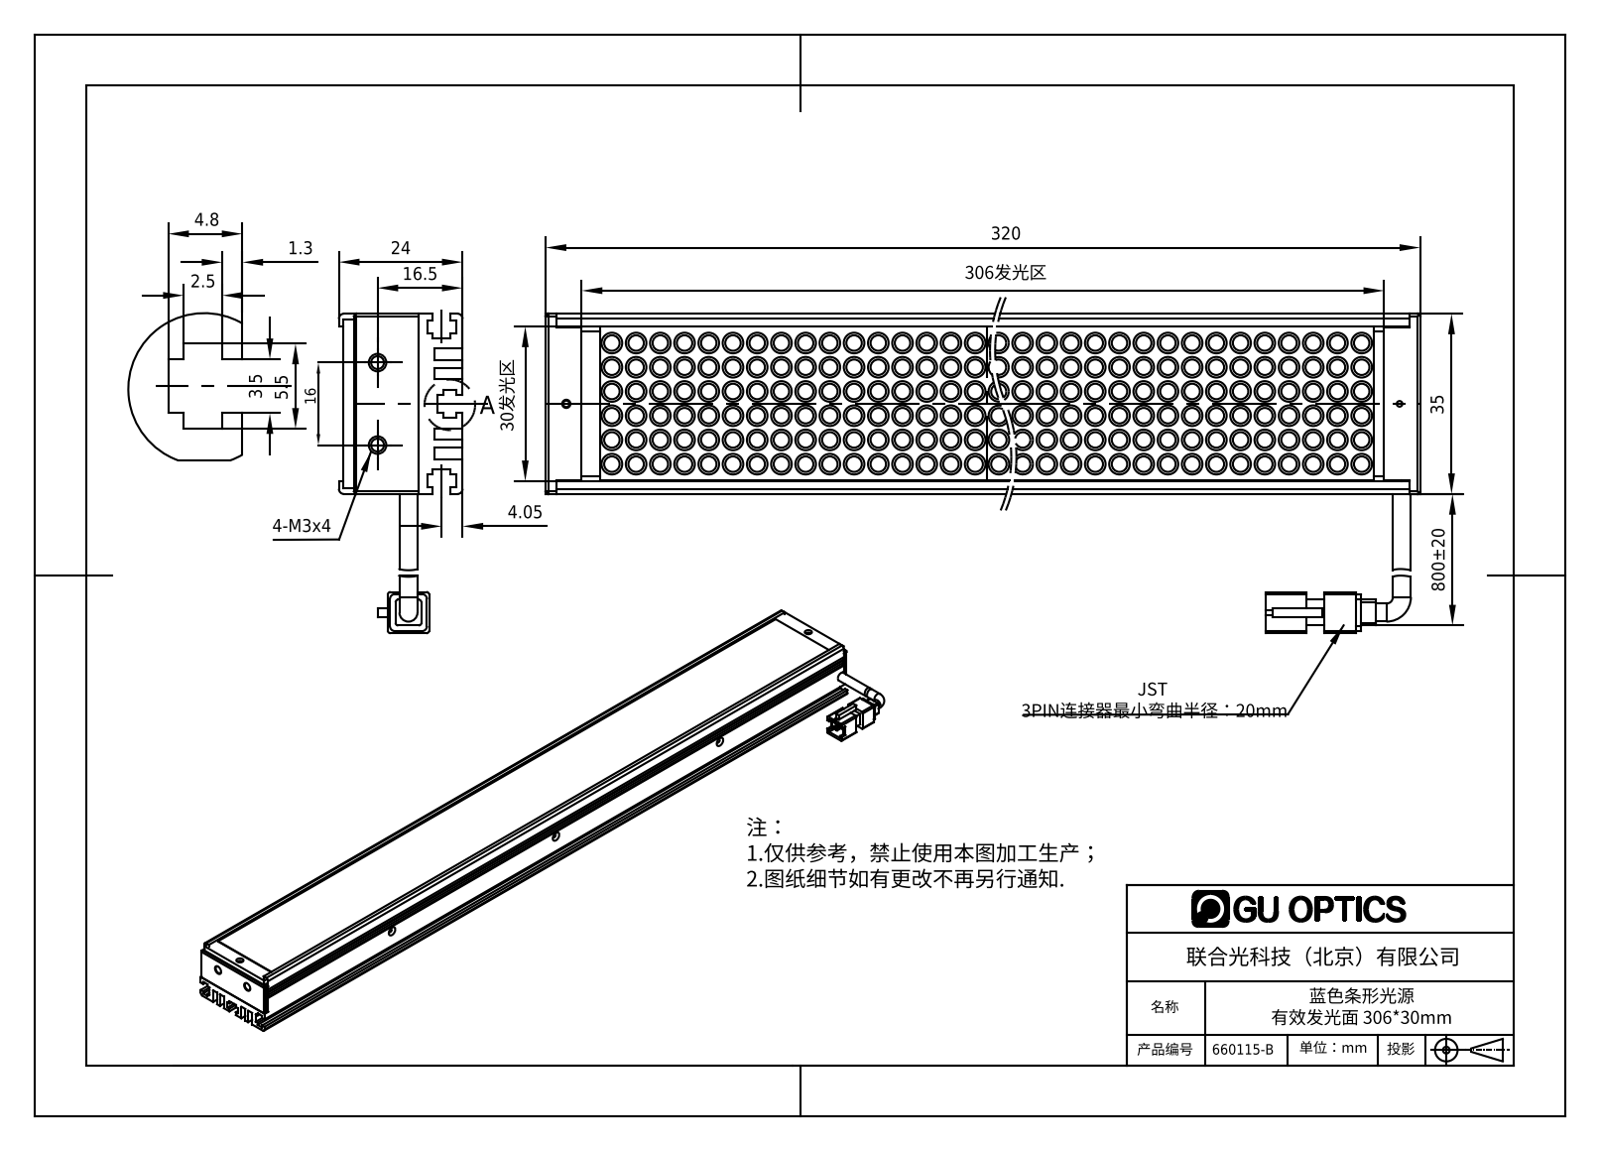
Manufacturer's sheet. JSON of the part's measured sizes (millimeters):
{"part_name": "660115-B", "step_written_by": "SolidWorks 2016 (AUTOMOTIVE_DESIGN)", "units": "millimeters", "bodies": {"solids": 11, "faces": 2871, "planar": 733, "cylindrical": 1647, "other": 491}, "overall_size": [320, 62, 24], "volume_mm3": 140705, "surface_area_mm2": 161979, "round_holes": [[1.6, 5], [1.7, 3], [1.5, 2], [2.5, 2], [2.8, 2], [3, 2], [1.1, 1], [1.25, 1], [2, 1]], "round_bosses_or_shafts": [[4, 384], [3, 384], [3.5, 2]], "partial_cylinders_radius": [[1, 28], [0.5, 8], [1.65, 1]], "face_to_face_distances": [2, 2.2, 11.2, 1, 2.5, 12.6, 14.6, 9.2, 14.8, 8.5], "hole_center_spacings": [312, 7, 66.02, 66.22, 90, 156.01, 156.09, 246.01]}
